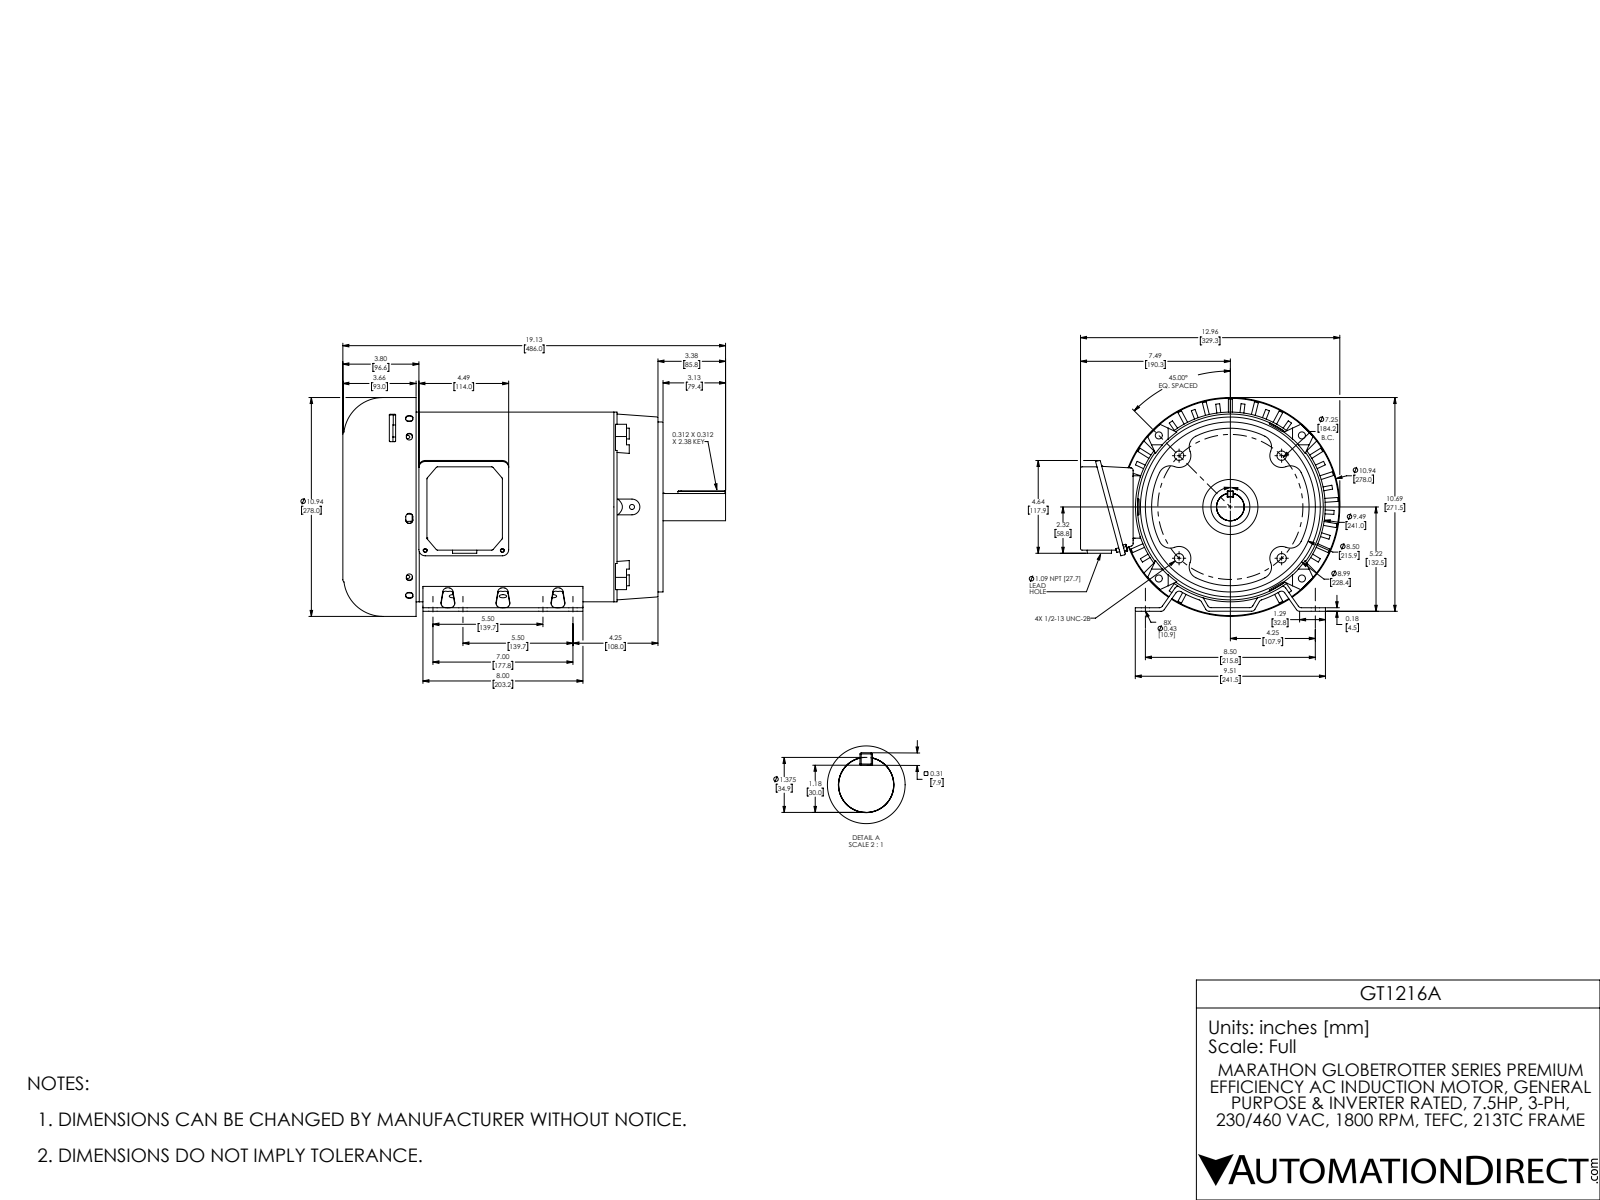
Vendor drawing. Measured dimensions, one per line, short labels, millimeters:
name: SS620688-213TC_Rev2 R1 Good Coord
written by: SolidWorks 2017 (AUTOMOTIVE_DESIGN)
unit: mm
bodies: 11 solids, 1927 faces (1137 planar, 572 cylindrical, 218 other)
size: 486 × 329.3 × 278
volume: 4 130 000 mm³; area: 1 325 000 mm²
holes: 10× ⌀9.4, 8× ⌀10.5, 5× ⌀8, 4× ⌀5.1, 4× ⌀6.4, 4× ⌀9, 4× ⌀12, 3× ⌀5.5, 2× ⌀12.7, 1× ⌀25, 1× ⌀33.5, 1× ⌀35.3
bosses: 2× ⌀5, 1× ⌀278, 1× ⌀241, 1× ⌀240.9, 1× ⌀237, 1× ⌀235.5, 1× ⌀215.9, 1× ⌀197
rounds: 53× R1.5, 36× R2.5, 35× R1.8, 16× R2, 16× R3, 16× R4.8, 12× R1, 12× R4.5
face distances: 4.5, 6, 345.9, 352.5, 6.6, 339.9, 346.5, 23.5, 1, 29.5
hole spacings: 158.1, 25.4, 36.4, 38.1, 39.8, 63.5, 88.9, 130.3
